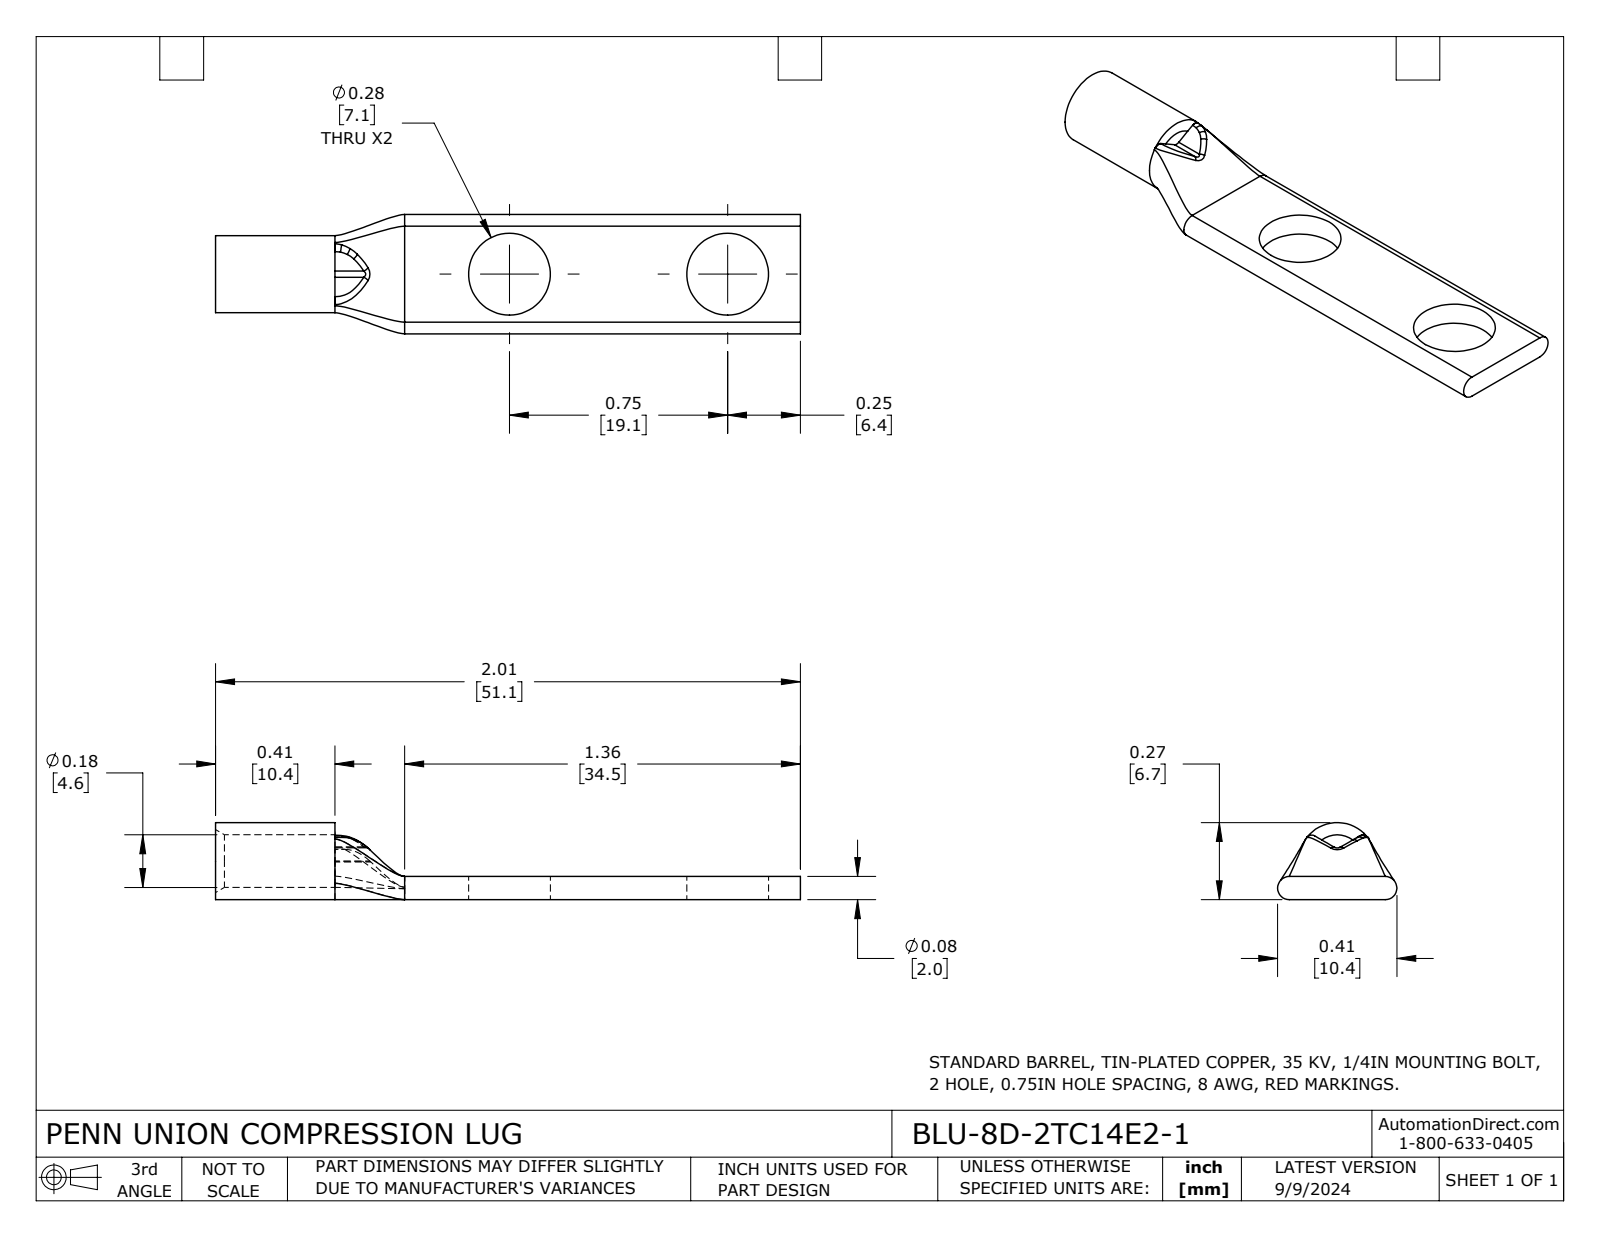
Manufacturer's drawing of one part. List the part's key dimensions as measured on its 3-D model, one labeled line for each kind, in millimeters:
Part name (STEP PRODUCT): BLU-8D-2TC14E2-1
STEP written by: SolidWorks 2023 (CONFIG_CONTROL_DESIGN)
Units: millimetres
Bodies: 1 solid, 42 faces (11 planar, 13 cylindrical, 18 other)
Overall size (bounding box): 51.1 × 10.4 × 6.7
Volume: 850 mm³ · Surface area: 1 390 mm²
Round holes (diameter × count): ⌀7.1 ×2, ⌀4.6 ×1
Round bosses / shafts (diameter × count): ⌀6.7 ×1
Partial cylindrical surfaces — rounded edges, fillets, slot ends (radius × count): R0.5 ×2, R1 ×2
Main face-to-face distances: 2, 51.1, 10.4, 40.6, 1.1, 16.5, 6.1, 34.5
Hole centre spacings: 19.1
